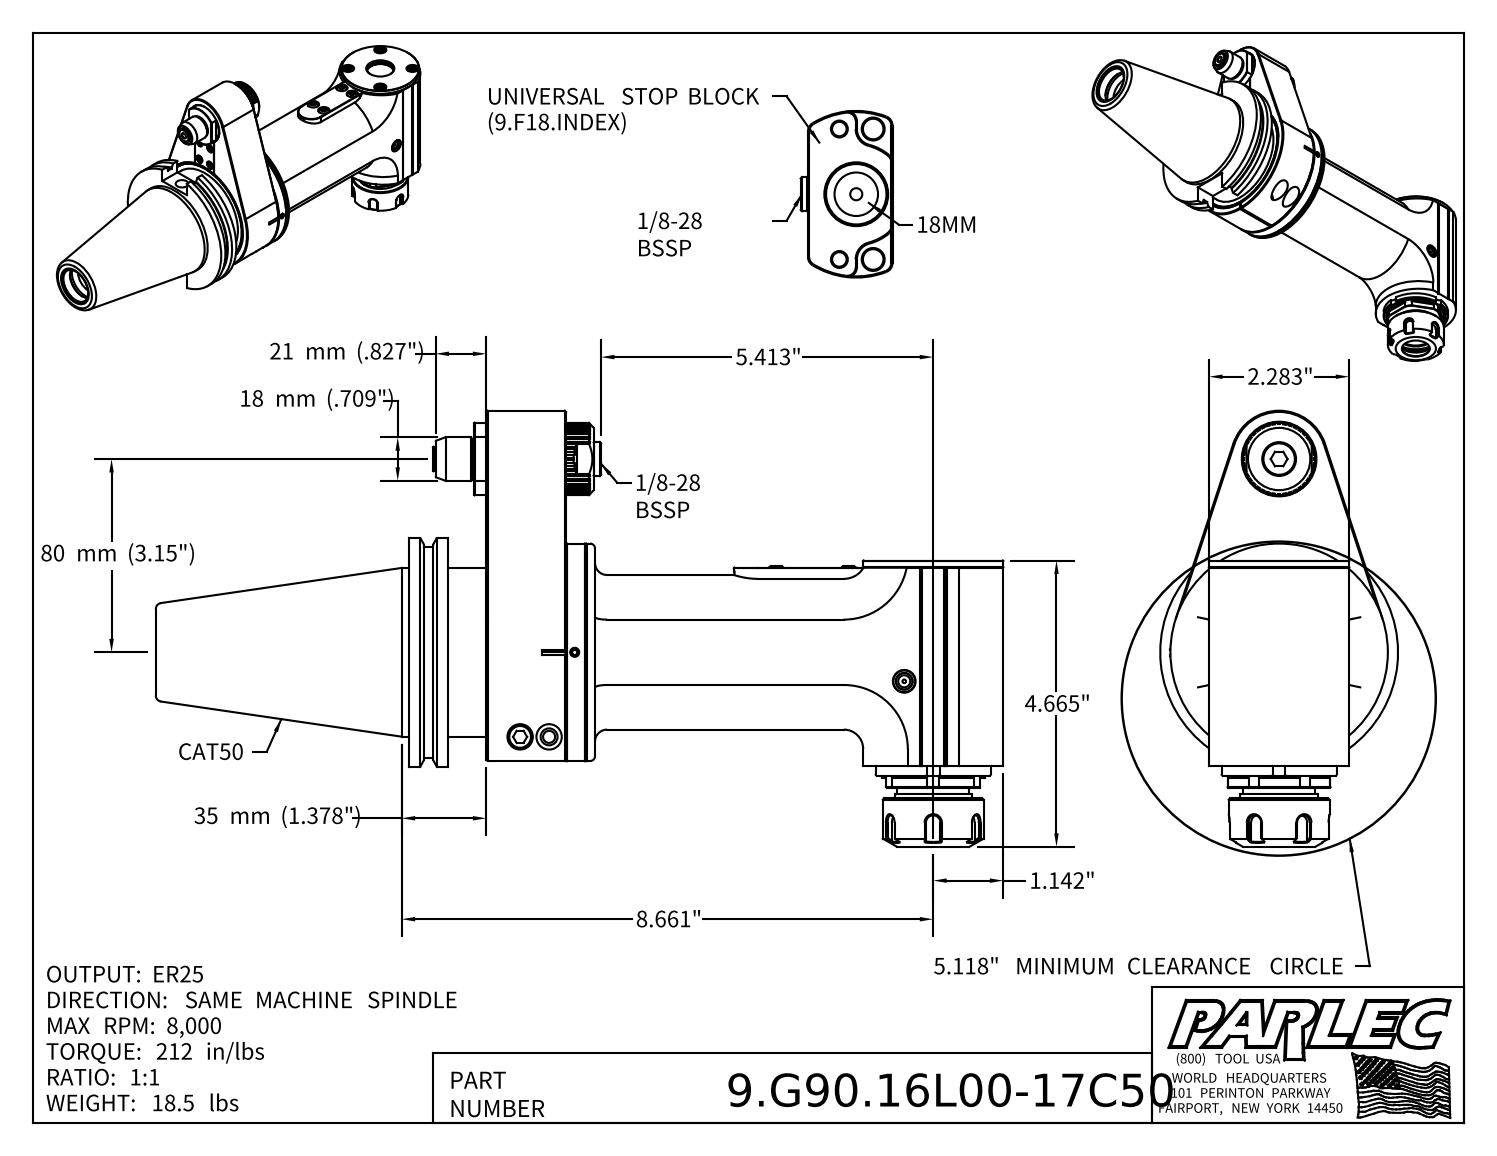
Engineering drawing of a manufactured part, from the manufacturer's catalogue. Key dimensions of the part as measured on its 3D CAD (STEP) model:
Part name (STEP PRODUCT): 9.G90.16L00-17C50; 9_G90_16L00; 9_GA1_458_1 (Classic, Type 1, Ca
STEP written by: Autodesk Inventor 2025 (AUTOMOTIVE_DESIGN)
Units: inches
Bodies: 4 solids, 1214 faces (772 planar, 200 cylindrical, 242 other)
Overall size (bounding box): 13.811 × 7.106 × 3.875
Volume: 84.28 in³ · Surface area: 279.2 in²
Round holes (diameter × count): ⌀0.165 ×6, ⌀0.118 ×4, ⌀0.13 ×4, ⌀0.236 ×4, ⌀0.315 ×4, ⌀0.197 ×3, ⌀0.157 ×2, ⌀0.276 ×2, ⌀0.335 ×2, ⌀0.413 ×2, ⌀0.354 ×1, ⌀0.433 ×1
Round bosses / shafts (diameter × count): ⌀0.295 ×4, ⌀0.394 ×3, ⌀3.875 ×1, ⌀3.593 ×1, ⌀3.543 ×1, ⌀3.071 ×1, ⌀2.75 ×1, ⌀2.283 ×1
Partial cylindrical surfaces — rounded edges, fillets, slot ends (radius × count): R0.118 ×8, R1.26 ×3, R0.085 ×2, R0.197 ×2, R0.394 ×2, R0.079 ×1, R0.092 ×1, R0.098 ×1
Main face-to-face distances: 1.299, 0.626, 0.315, 0.984, 2.283, 1.252, 1.925, 0.941, 2.551, 1.567
Hole centre spacings: 1.476, 2.557, 0.433, 0.366, 0.551, 0.764, 0.78, 1.395
